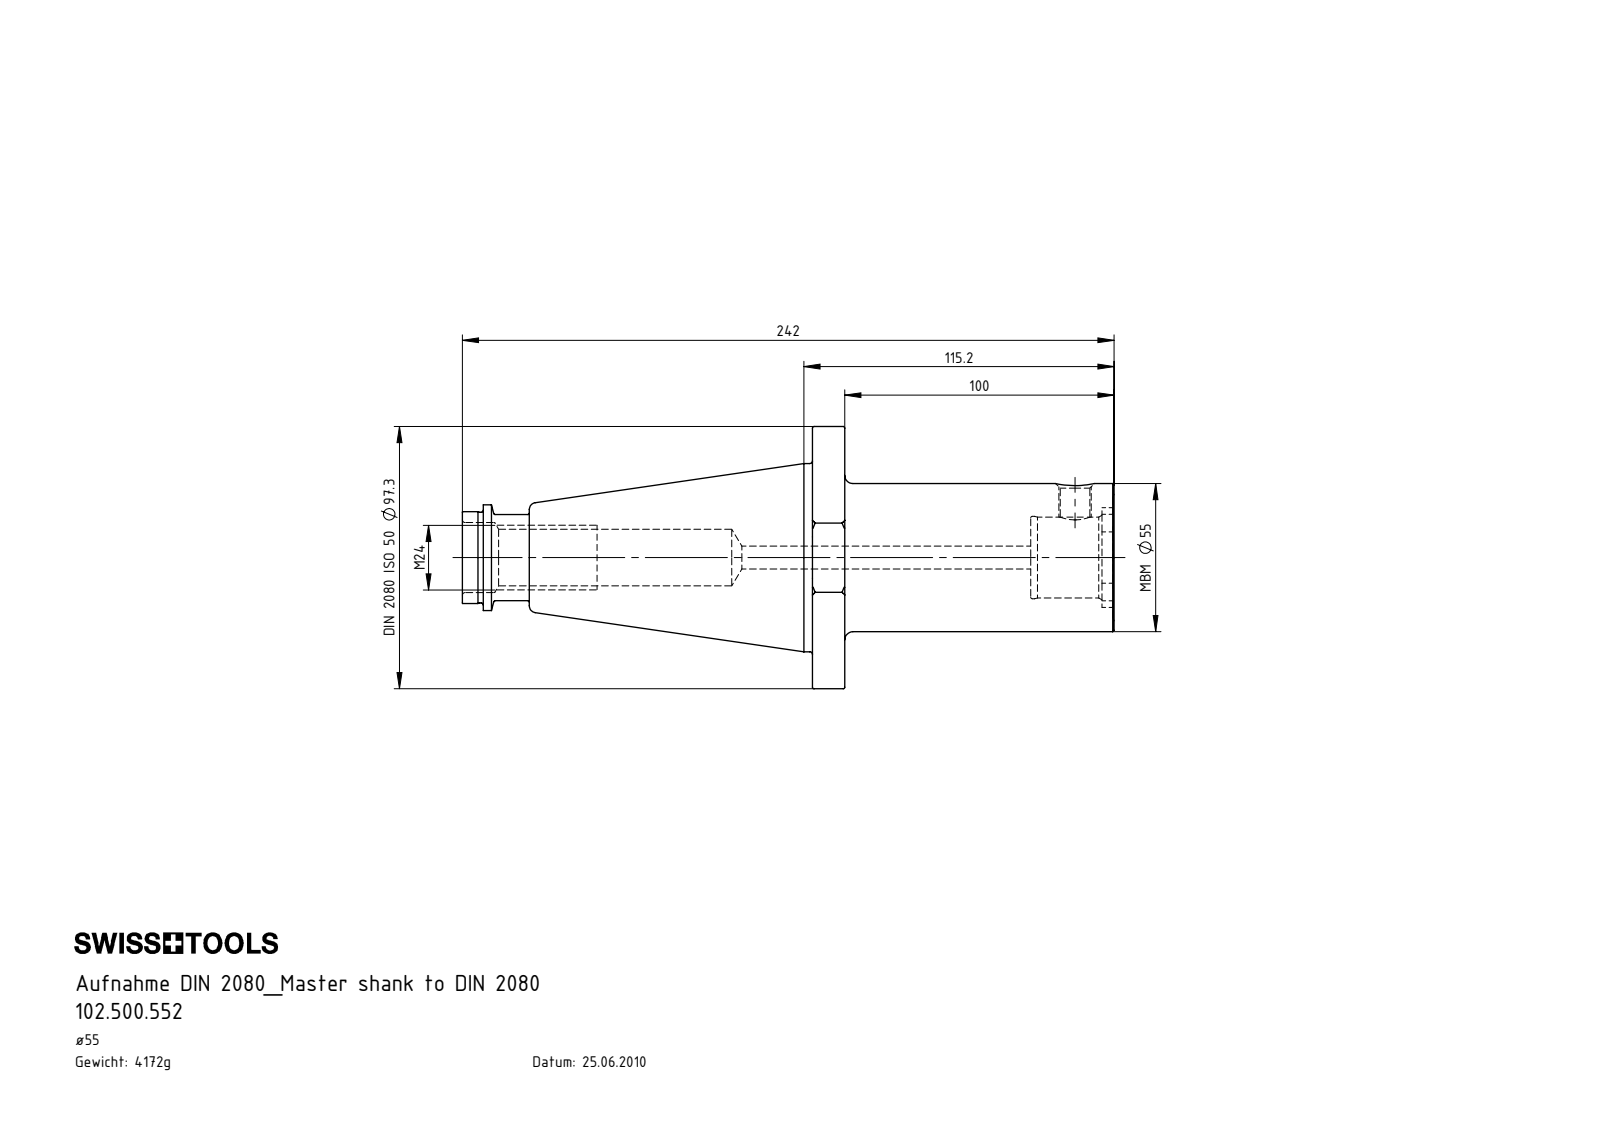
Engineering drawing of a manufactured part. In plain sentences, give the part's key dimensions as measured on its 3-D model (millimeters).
The part is named "MB5-ER1.001.017_A; SZ5-MB5.K01.115_C; 102.500.552". Its 3-D file was written by "SolidWorks 2017 (CONFIG_CONTROL_DESIGN)". It is 2 solids with 158 faces: 47 planar, 53 cylindrical and 58 other. Overall it measures 242 by 97.3 by 93.84 millimeters. Its volume is 532 844 cubic millimeters and its surface area 67 250 square millimeters. Round holes: 1 of diameter 6, 1 of diameter 8.5, 1 of diameter 11, 1 of diameter 21, 1 of diameter 26, 1 of diameter 30, 1 of diameter 30.6. Round bosses or shafts: 1 of diameter 97.3, 1 of diameter 69.85, 1 of diameter 55, 1 of diameter 39.24, 1 of diameter 34.05, 1 of diameter 33.65, 1 of diameter 32, 1 of diameter 12. Partial cylindrical surfaces (rounded edges, fillets, slot ends): 12 of radius 2, 4 of radius 5.2, 1 of radius 18.5, 1 of radius 21.27. The main face-to-face distances are 12, 81, 69, 112, 100, 31, 107.45, 95.45, 26.45, 4.55.
